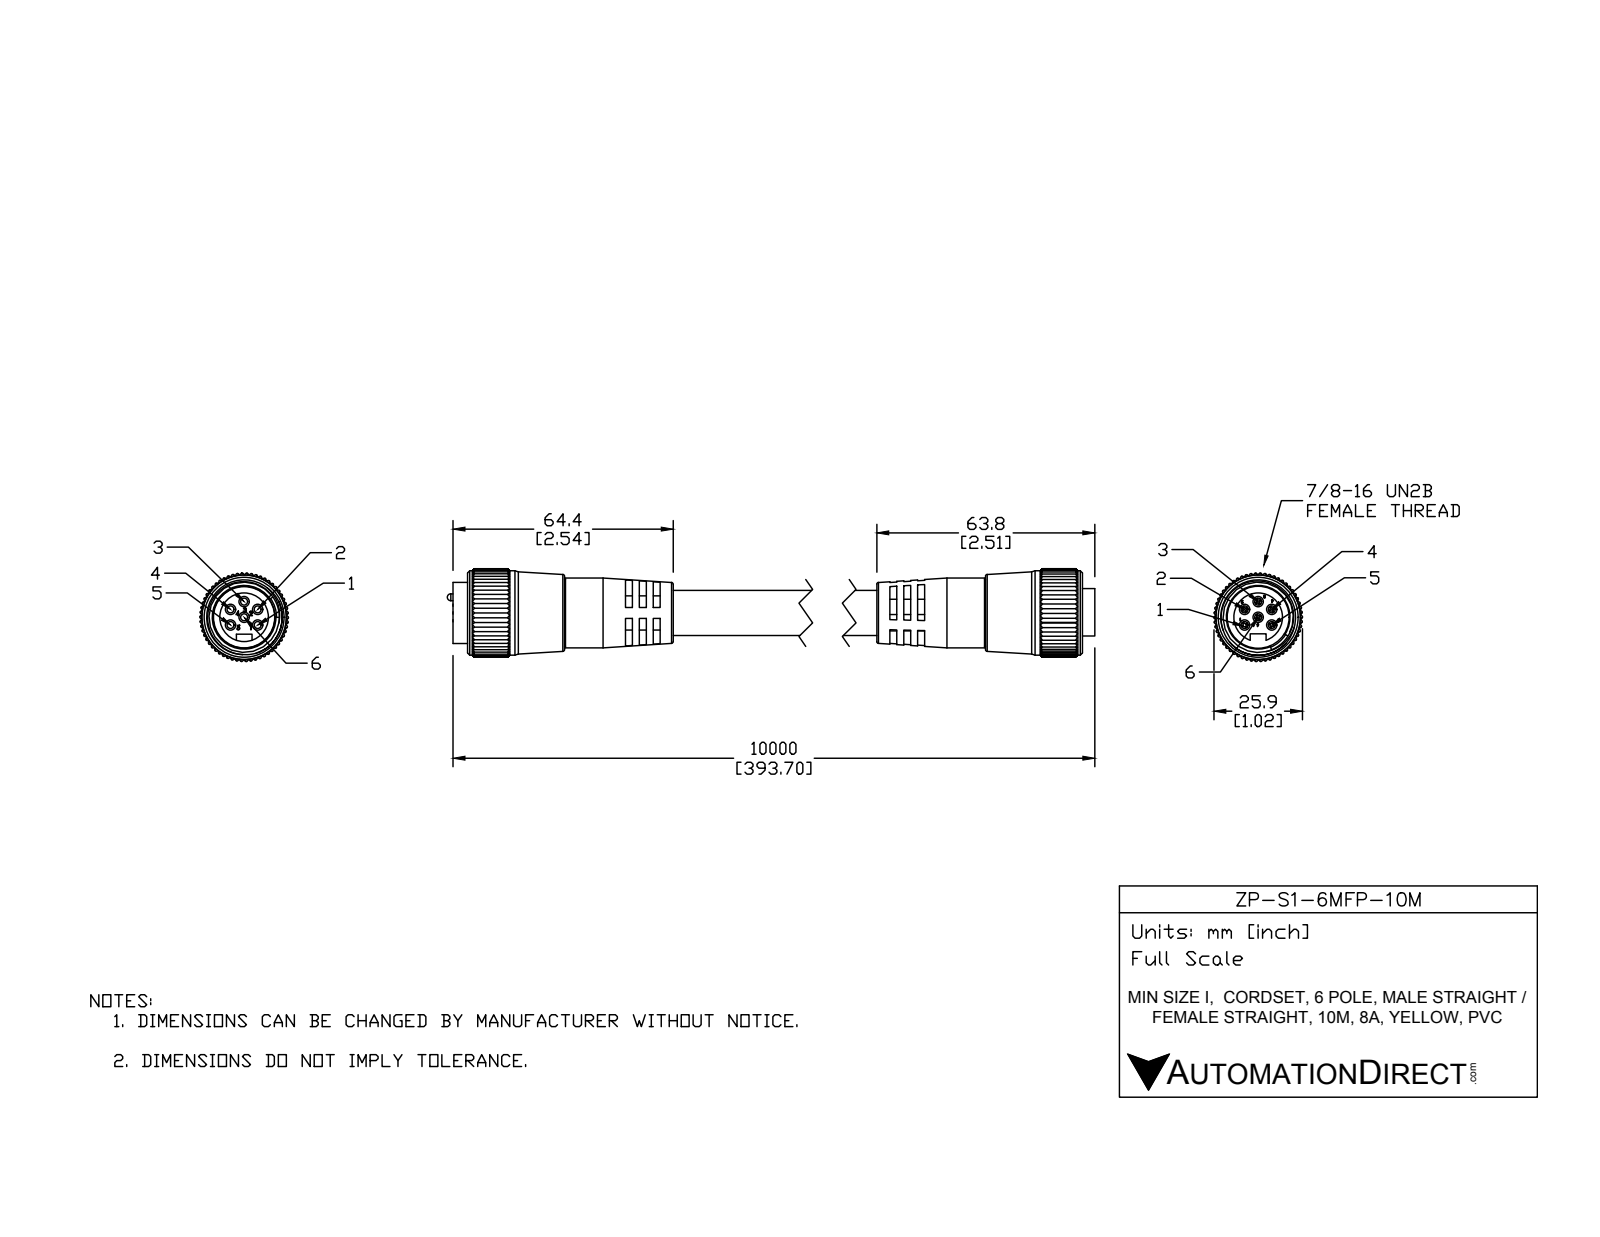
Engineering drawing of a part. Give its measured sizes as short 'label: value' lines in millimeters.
name: ZP-S1-6MFP-10M
written by: SolidWorks 2015 (AUTOMOTIVE_DESIGN)
unit: mm
bodies: 10 solids, 1226 faces (452 planar, 636 cylindrical, 138 other)
size: 229.66 × 25.84 × 25.83
volume: 50 878 mm³; area: 23 497 mm²
holes: 6× ⌀3.05, 1× ⌀19.96, 1× ⌀20.45, 1× ⌀21
bosses: 6× ⌀2, 1× ⌀24.68, 1× ⌀20.4, 1× ⌀19.5, 1× ⌀17.88, 1× ⌀14.22, 1× ⌀9.91, 1× ⌀3.05
rounds: 165× R0.25, 1× R2.29, 1× R5.25, 1× R12.93
face distances: 2, 4.02, 117.68, 113.65, 4.03, 125.74, 59.84, 4.04, 121.7, 121.72
hole spacings: 4.57, 4.56, 7.91, 7.92, 9.14
